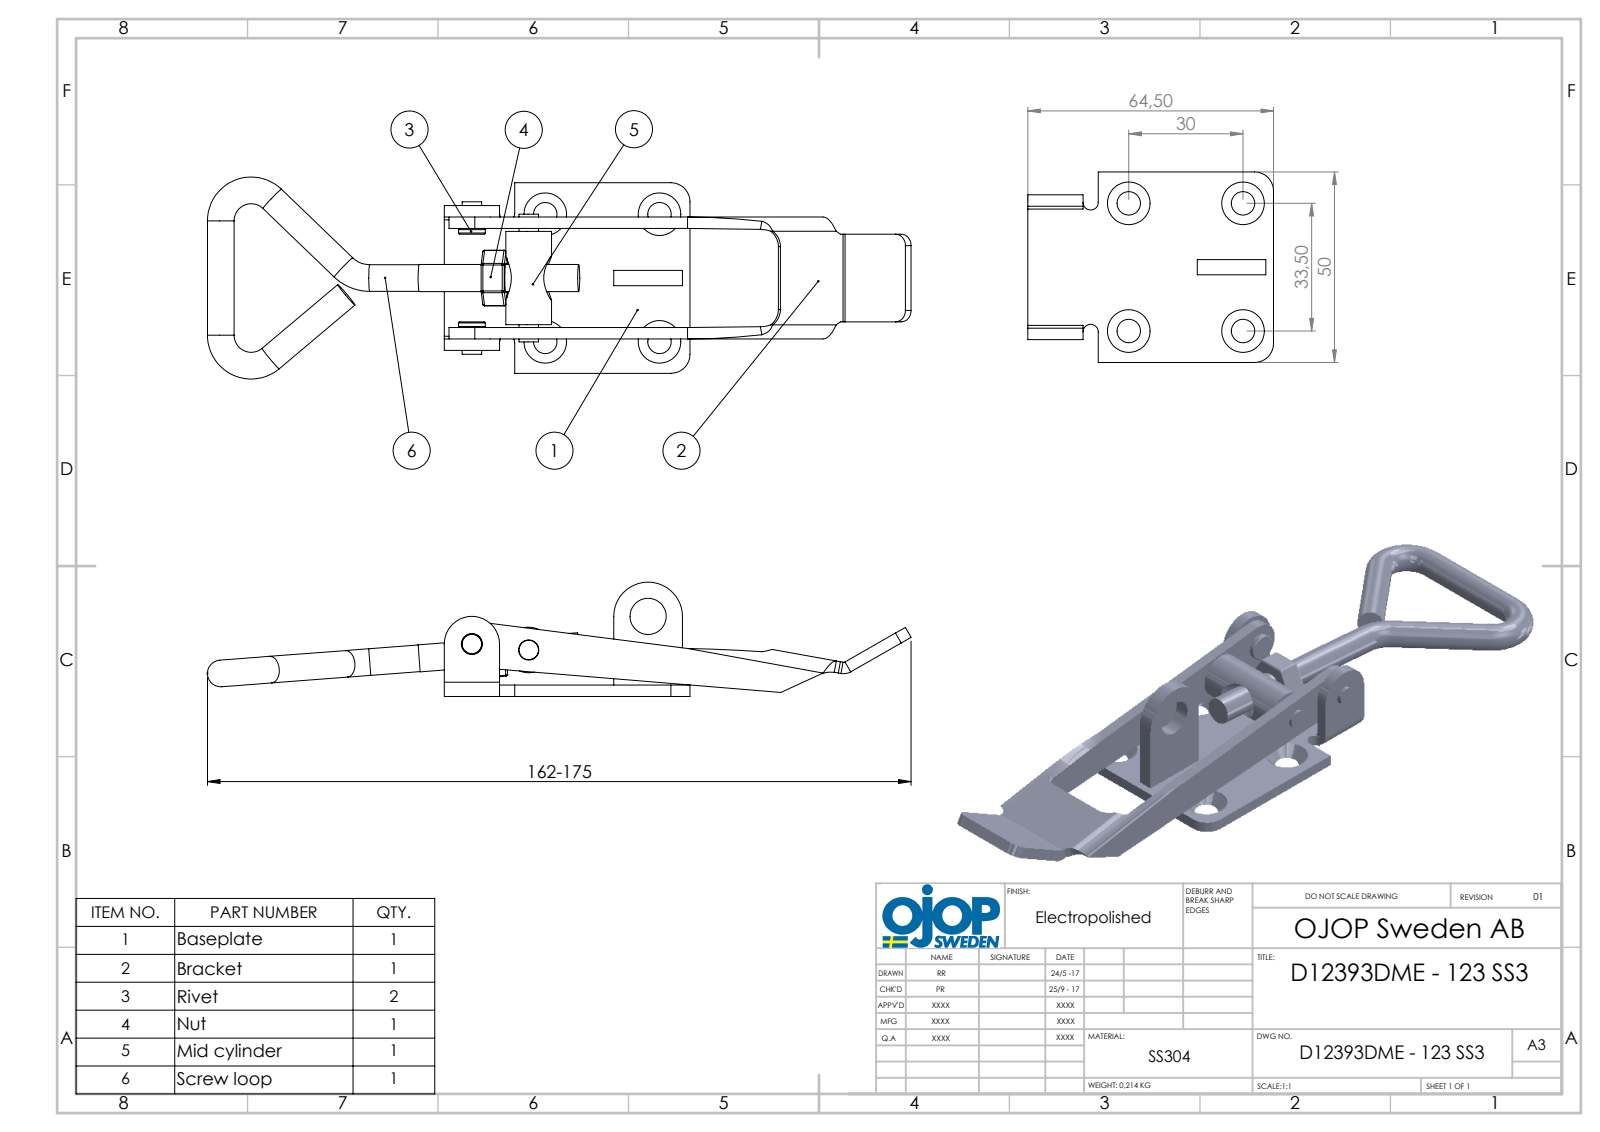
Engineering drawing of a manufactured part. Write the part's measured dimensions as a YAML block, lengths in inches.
part_name: "rulle; mutter; nit; bygel (+3 more)"
step_written_by: "SolidWorks 2015 (AUTOMOTIVE_DESIGN)"
units: inches
bodies: {solids: 7, faces: 204, planar: 71, cylindrical: 83, other: 50}
overall_size: [7.272, 2.087, 1.181]
volume: 1.81
surface_area: 34.64
round_holes:
  - {diameter: 0.209, count: 2}
  - {diameter: 0.217, count: 1}
  - {diameter: 0.268, count: 1}
  - {diameter: 0.276, count: 1}
  - {diameter: 0.374, count: 1}
round_bosses_or_shafts:
  - {diameter: 0.276, count: 5}
  - {diameter: 0.201, count: 2}
  - {diameter: 0.472, count: 1}
  - {diameter: 0.28, count: 1}
partial_cylinders:
  - {radius: 0.02, count: 18}
  - {radius: 0.029, count: 5}
  - {radius: 0.147, count: 5}
  - {radius: 0.197, count: 4}
  - {radius: 0.079, count: 2}
  - {radius: 0.118, count: 2}
  - {radius: 0.236, count: 1}
  - {radius: 0.285, count: 1}
face_to_face_distances: [0.118, 1.142, 1.26, 1.024, 0.709, 0.551, 0.433, 0.591, 0.236, 0.157]
hole_center_spacings: [0.591, 1.281, 1.843]
